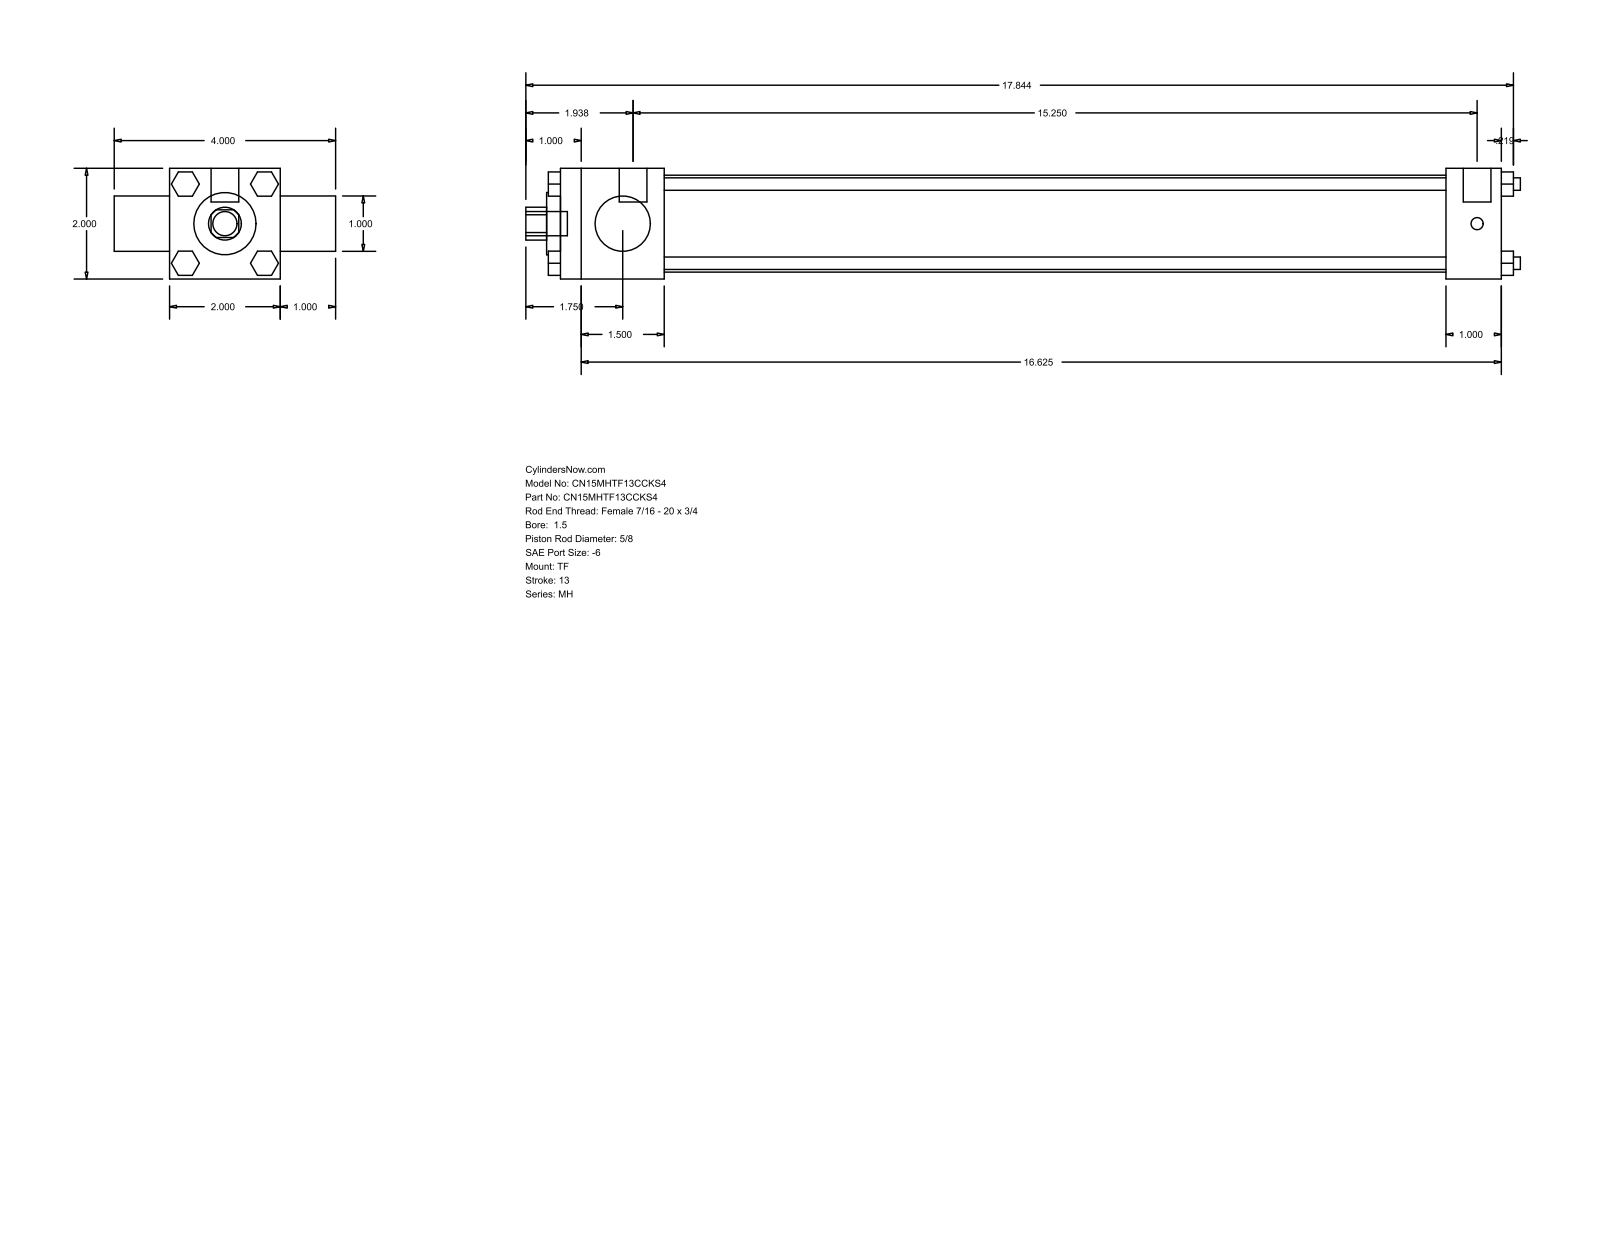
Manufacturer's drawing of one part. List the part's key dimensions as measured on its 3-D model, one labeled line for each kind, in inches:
Part name (STEP PRODUCT): MH_TF__0150_0.625
STEP written by: GSSL Pune (CONFIG_CONTROL_DESIGN)
Units: inches
Bodies: 0 solids, 120 faces (92 planar, 28 cylindrical, 0 other)
Overall size (bounding box): 17.969 × 4 × 2
Round holes (diameter × count): ⌀0.625 ×1, ⌀1 ×1, ⌀1.125 ×1, ⌀1.75 ×1
Round bosses / shafts (diameter × count): ⌀0.225 ×4, ⌀0.219 ×3, ⌀0.5 ×2, ⌀0.437 ×1
Partial cylindrical surfaces — rounded edges, fillets, slot ends (radius × count): R0.297 ×1
Main face-to-face distances: 2, 17, 1, 3, 1.875, 15.125, 16, 14.125, 1, 0.437
